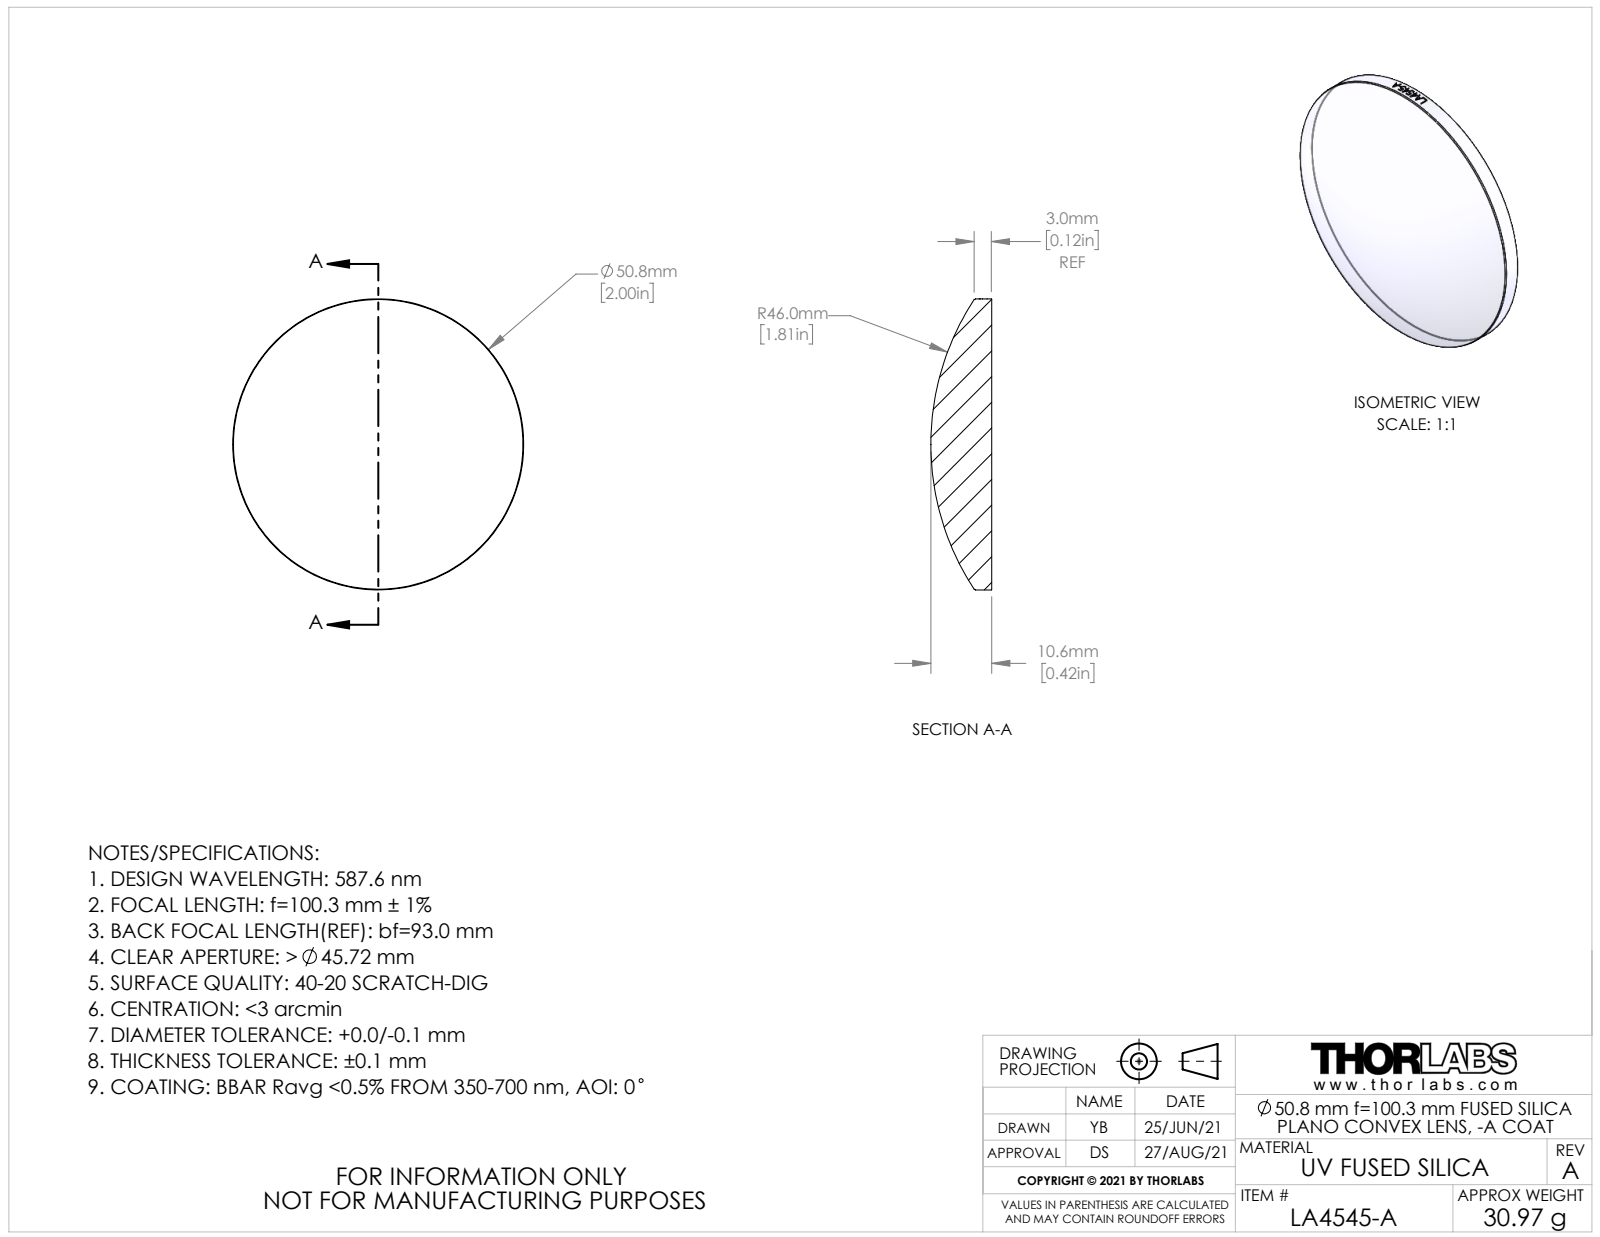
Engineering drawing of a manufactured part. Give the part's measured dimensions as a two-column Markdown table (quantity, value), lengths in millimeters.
| quantity | value |
| --- | --- |
| part name | CTN017537-E0W; CTN017565 |
| STEP written by | SolidWorks 2018 (AUTOMOTIVE_DESIGN) |
| units | millimeters |
| bodies | 1 solid, 21 faces (1 planar, 14 cylindrical, 6 other) |
| overall size | 50.8 × 50.8 × 10.64 |
| volume | 14 057 mm³ |
| surface area | 4 701 mm² |
| round bosses / shafts (diameter × count) | 50.8 × 1 |
